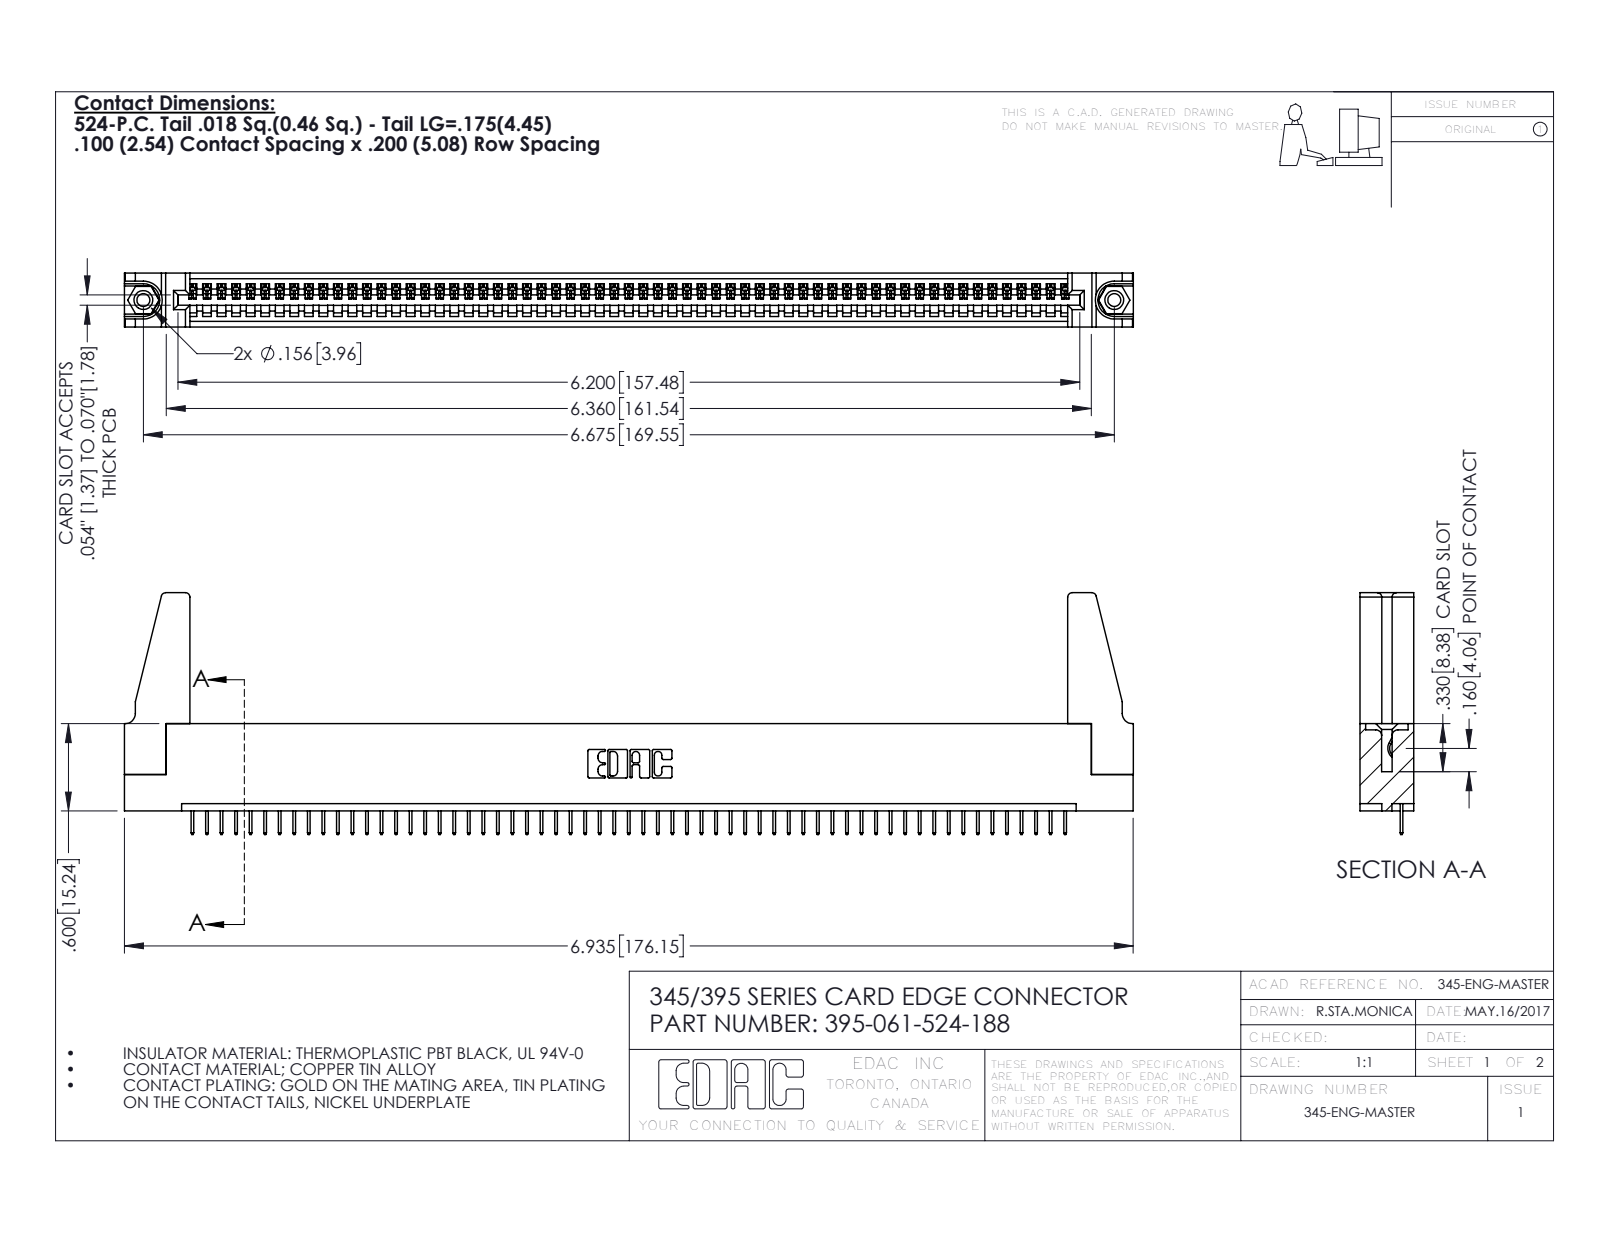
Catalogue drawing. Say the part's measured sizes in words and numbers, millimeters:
The part is named "345-220-078_345-220-088; 345-292-001_345-293-124; 345 Part_Flush Mounting Lugs - 0.156 Dia-TH; 345-250-001_345-250-001-102 (+1 more)". Its 3-D file was written by "SolidWorks 2016 (CONFIG_CONTROL_DESIGN)". It is 66 solids with 4032 faces: 2958 planar, 1058 cylindrical and 16 other. Overall it measures 176.2 by 42.2 by 9.4 millimeters. Its volume is 19 890 cubic millimeters and its surface area 24 740 square millimeters. Round holes: 2 of diameter 2.3, 2 of diameter 3.2, 2 of diameter 4, 1 of diameter 1.6. Round bosses or shafts: 2 of diameter 3.9. Partial cylindrical surfaces (rounded edges, fillets, slot ends): 122 of radius 0.2, 22 of radius 0.3, 8 of radius 0.8, 6 of radius 0.2, 6 of radius 0.8, 3 of radius 0.7, 2 of radius 0.8, 2 of radius 1. The main face-to-face distances are 1.8, 7.6, 9.4, 5.1, 2.5, 6.9, 0.6, 5.7, 1.8, 3.8. The hole center spacings are 6.9, 163.6, 169.5.
